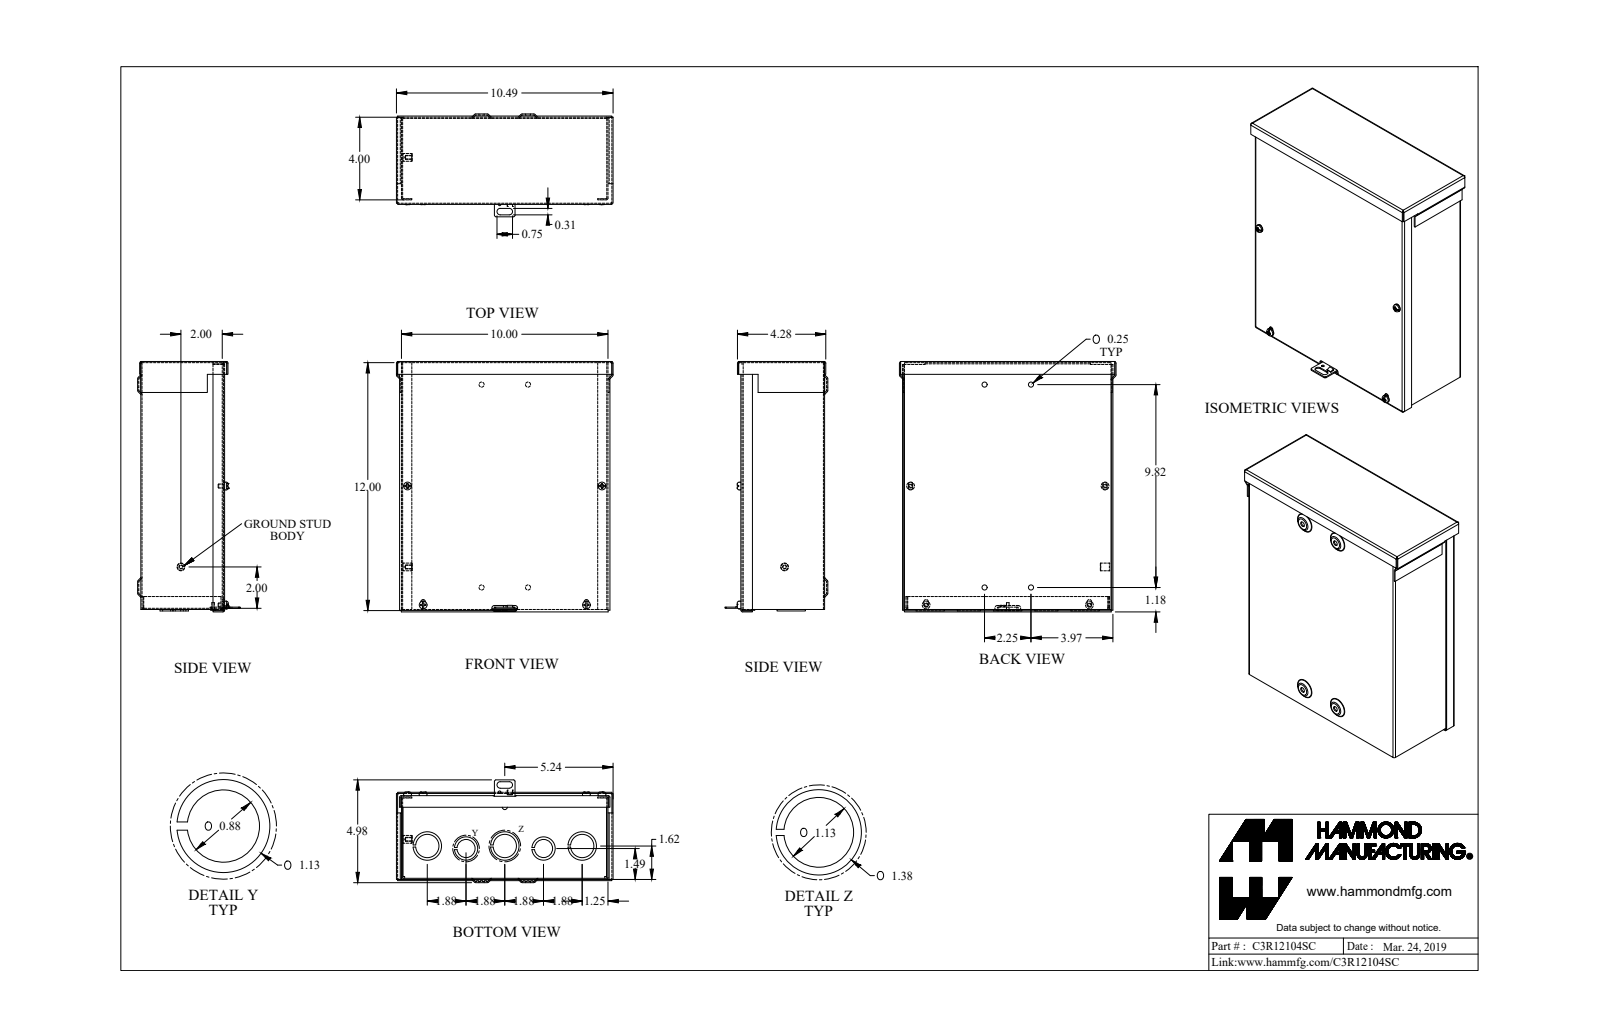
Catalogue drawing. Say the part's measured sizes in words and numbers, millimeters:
The part is named "C3R12104SC_Default". Its 3-D file was written by "SolidWorks 2019 (CONFIG_CONTROL_DESIGN)". It is 11 solids with 429 faces: 226 planar, 117 cylindrical and 86 other. Overall it measures 307.8 by 266.4 by 126.4 millimeters. Its volume is 457 700 cubic millimeters and its surface area 636 800 square millimeters. Round holes: 4 of diameter 4.3, 4 of diameter 6.4, 3 of diameter 28.6, 2 of diameter 22.2, 1 of diameter 3.2, 1 of diameter 3.5, 1 of diameter 4. Round bosses or shafts: 4 of diameter 9.5, 4 of diameter 4.8, 2 of diameter 34.9, 2 of diameter 28.6, 1 of diameter 34.9, 1 of diameter 9.5, 1 of diameter 3.2. Partial cylindrical surfaces (rounded edges, fillets, slot ends): 21 of radius 0.7, 21 of radius 2.2, 8 of radius 3.2, 4 of radius 2.7, 4 of radius 2.8, 2 of radius 4. The main face-to-face distances are 1.4, 101.6, 100.2, 103, 252.6, 1.4, 254, 251.1, 301.9, 303.4. The hole center spacings are 154.4, 193.6, 95.3, 47.7, 47.8, 57.2, 74.8, 106.6.
